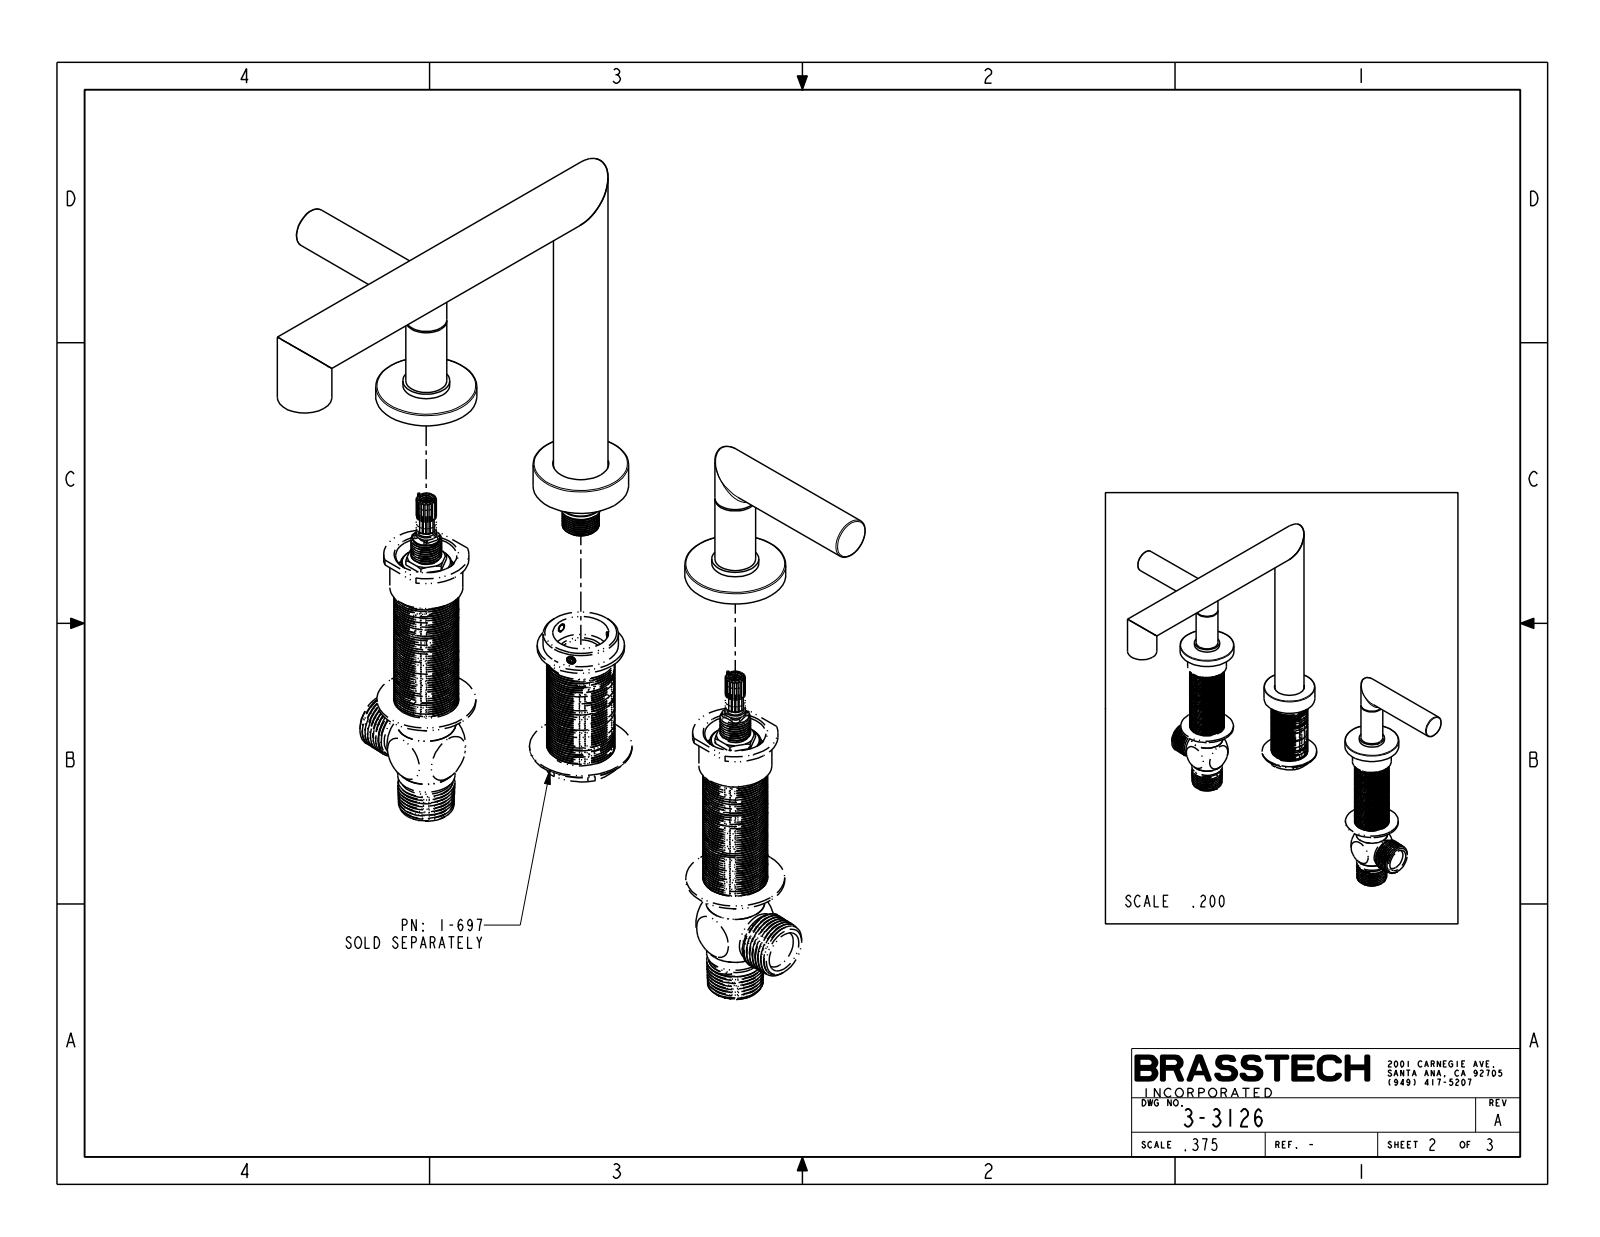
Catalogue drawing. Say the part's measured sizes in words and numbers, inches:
The part is named "3-3126". Its 3-D file was written by "CREO PARAMETRIC BY PTC INC, 2018400 (CONFIG_CONTROL_DESIGN)". It is 3 solids with 85 faces: 23 planar, 36 cylindrical and 26 other. Overall it measures 14 by 8.575 by 7.064 inches. Its volume is 18.19 cubic inches and its surface area 92.88 square inches. Round bosses or shafts: 3 of diameter 1, 3 of diameter 0.75, 2 of diameter 1.85, 2 of diameter 0.86, 2 of diameter 0.506, 1 of diameter 1.75. The main face-to-face distances are 0.25, 0.5, 5.563, 5.313, 5.063, 1.701, 1.732, 1.451, 1.482, 1.201.
